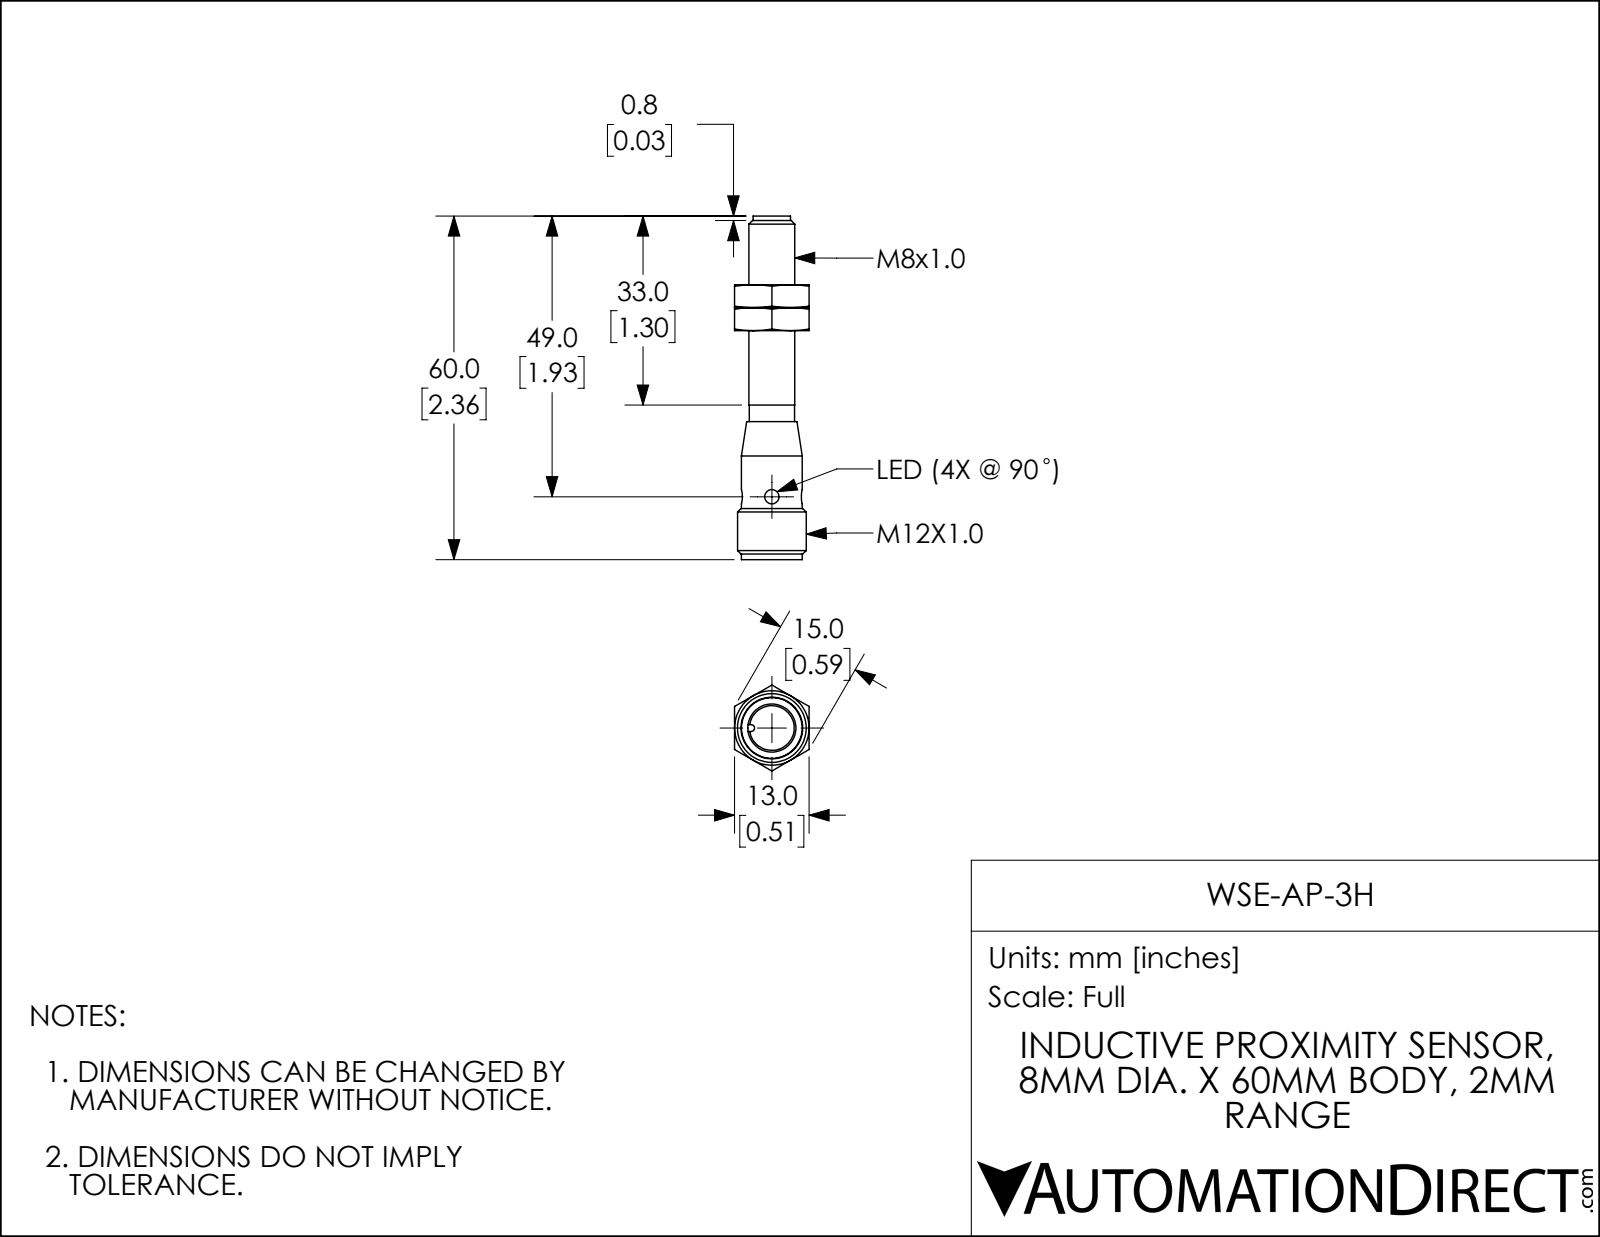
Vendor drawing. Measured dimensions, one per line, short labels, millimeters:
name: WSE-AP-3H
written by: SolidWorks 2017 (AUTOMOTIVE_DESIGN)
unit: mm
bodies: 3 solids, 78 faces (27 planar, 14 cylindrical, 37 other)
size: 60 × 15 × 13
volume: 4 380 mm³; area: 3 073 mm²
holes: 2× ⌀2.5, 1× ⌀6.9, 1× ⌀8.4
bosses: 1× ⌀12, 1× ⌀10.6, 1× ⌀8, 1× ⌀7.9, 1× ⌀6.6
rounds: 1× R0.6
face distances: 13, 4, 8, 35.1, 31.1, 39.1, 51.1, 20, 16, 12
